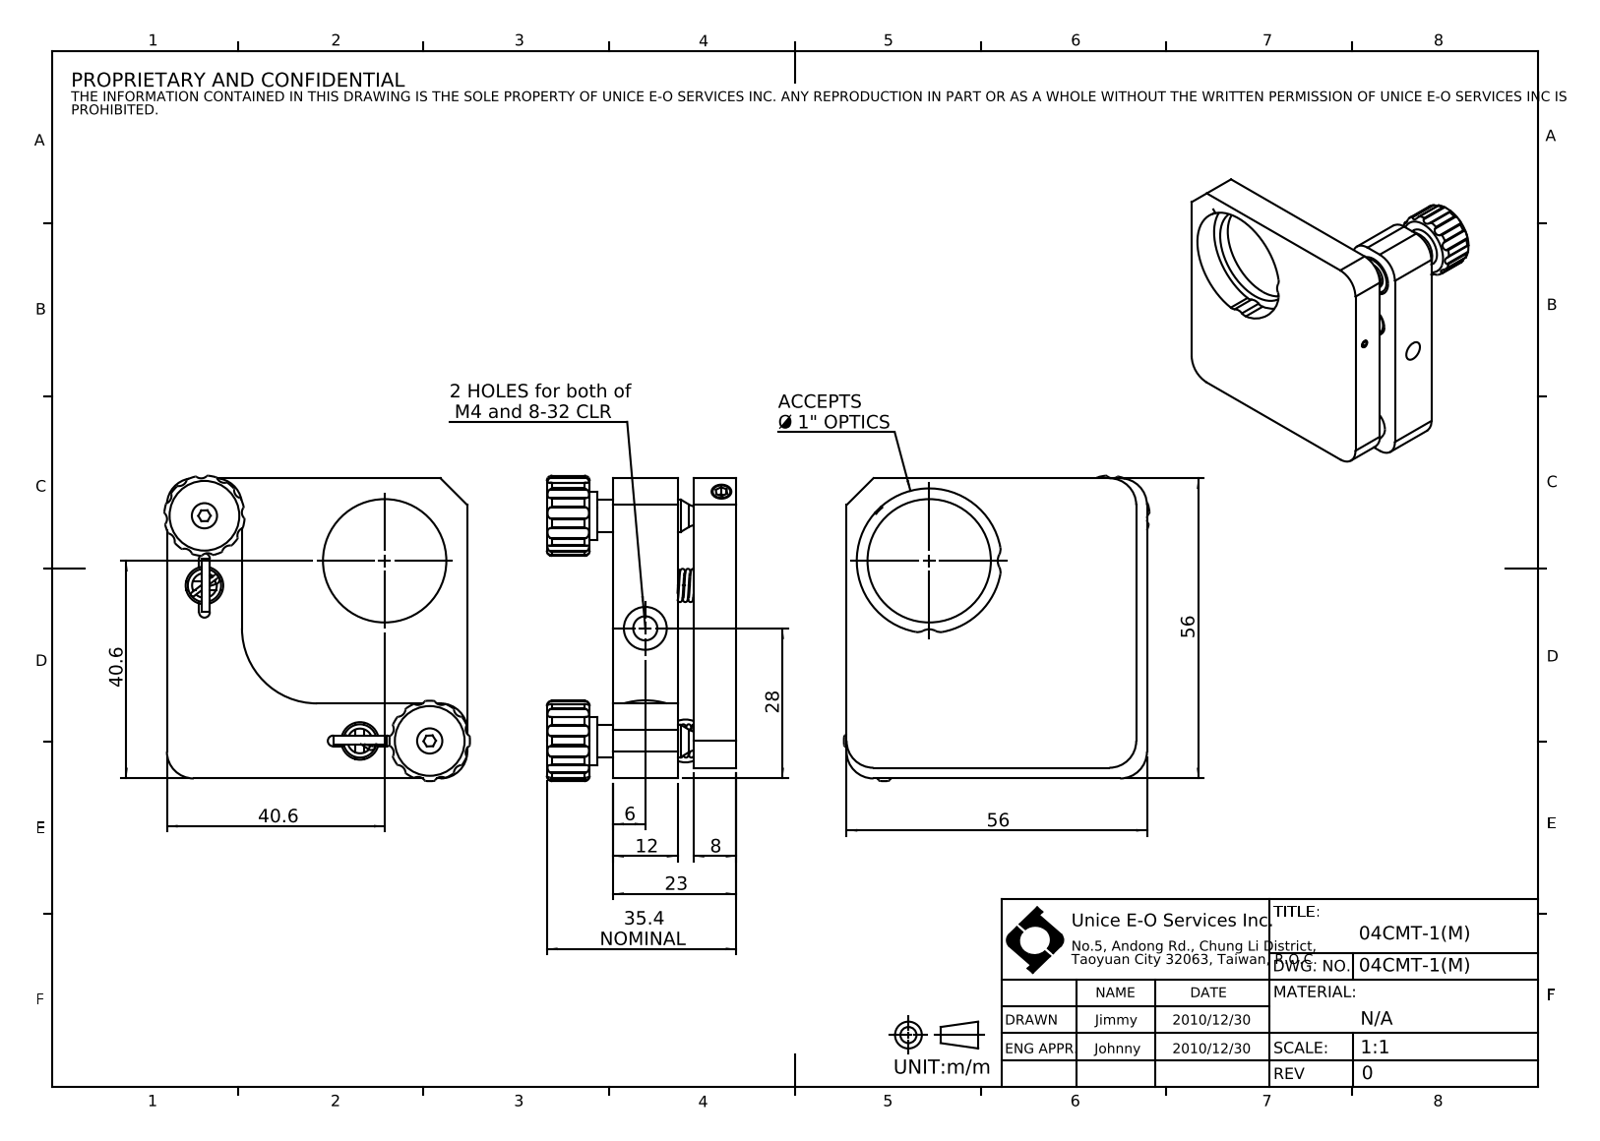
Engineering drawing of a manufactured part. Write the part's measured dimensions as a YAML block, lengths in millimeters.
part_name: "04CMT-1(M)"
step_written_by: "SolidWorks 2016 (CONFIG_CONTROL_DESIGN)"
units: millimeters
bodies: {solids: 22, faces: 425, planar: 113, cylindrical: 233, other: 79}
overall_size: [56.97, 56.97, 35.36]
volume: 36432
surface_area: 20318
round_holes:
  - {diameter: 1.2, count: 4}
  - {diameter: 1.7, count: 2}
  - {diameter: 4, count: 2}
  - {diameter: 4.5, count: 2}
  - {diameter: 4.7, count: 2}
  - {diameter: 5.9, count: 2}
  - {diameter: 6, count: 2}
  - {diameter: 7, count: 2}
  - {diameter: 8, count: 2}
  - {diameter: 9.5, count: 2}
  - {diameter: 1.5, count: 1}
  - {diameter: 3.3, count: 1}
round_bosses_or_shafts:
  - {diameter: 1.6, count: 5}
  - {diameter: 9, count: 2}
  - {diameter: 1.5, count: 2}
  - {diameter: 0.8, count: 2}
  - {diameter: 4, count: 1}
partial_cylinders:
  - {radius: 0.3, count: 48}
  - {radius: 1.5, count: 25}
  - {radius: 5, count: 8}
  - {radius: 0.75, count: 4}
  - {radius: 1, count: 4}
  - {radius: 2, count: 4}
  - {radius: 2.5, count: 2}
  - {radius: 7.5, count: 2}
face_to_face_distances: [8, 12, 3, 15, 23, 11, 56, 2, 54, 14]
hole_center_spacings: [13, 16.12, 21.24, 33.91, 34.12, 34.63, 51.04, 41.01]
